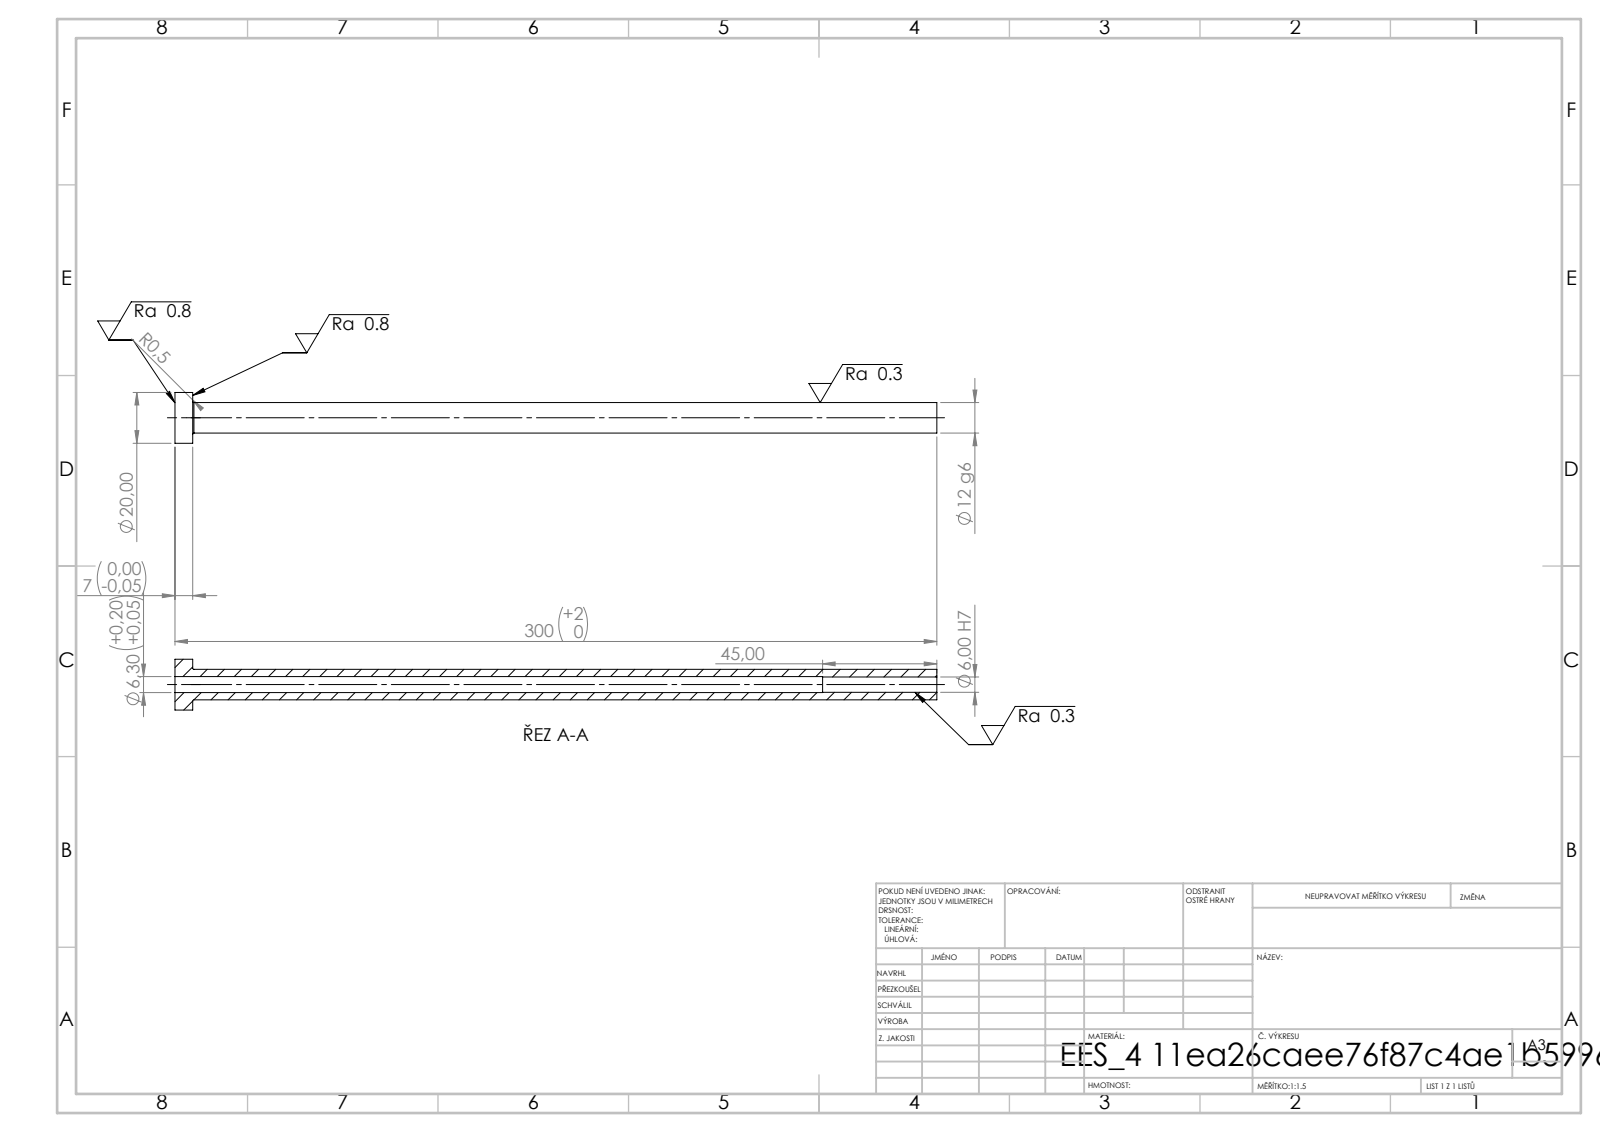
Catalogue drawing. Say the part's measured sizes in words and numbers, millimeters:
Its 3-D file was written by "SolidWorks 2019 (CONFIG_CONTROL_DESIGN)". It is 1 solid with 14 faces: 4 planar, 8 cylindrical and 2 other. Overall it measures 300 by 20 by 20 millimeters. Its volume is 26 117 cubic millimeters and its surface area 17 945 square millimeters. Round holes: 1 of diameter 6, 1 of diameter 6.3. Round bosses or shafts: 1 of diameter 20, 1 of diameter 12. The main face-to-face distances are 7, 300, 293, 255, 248, 45.
